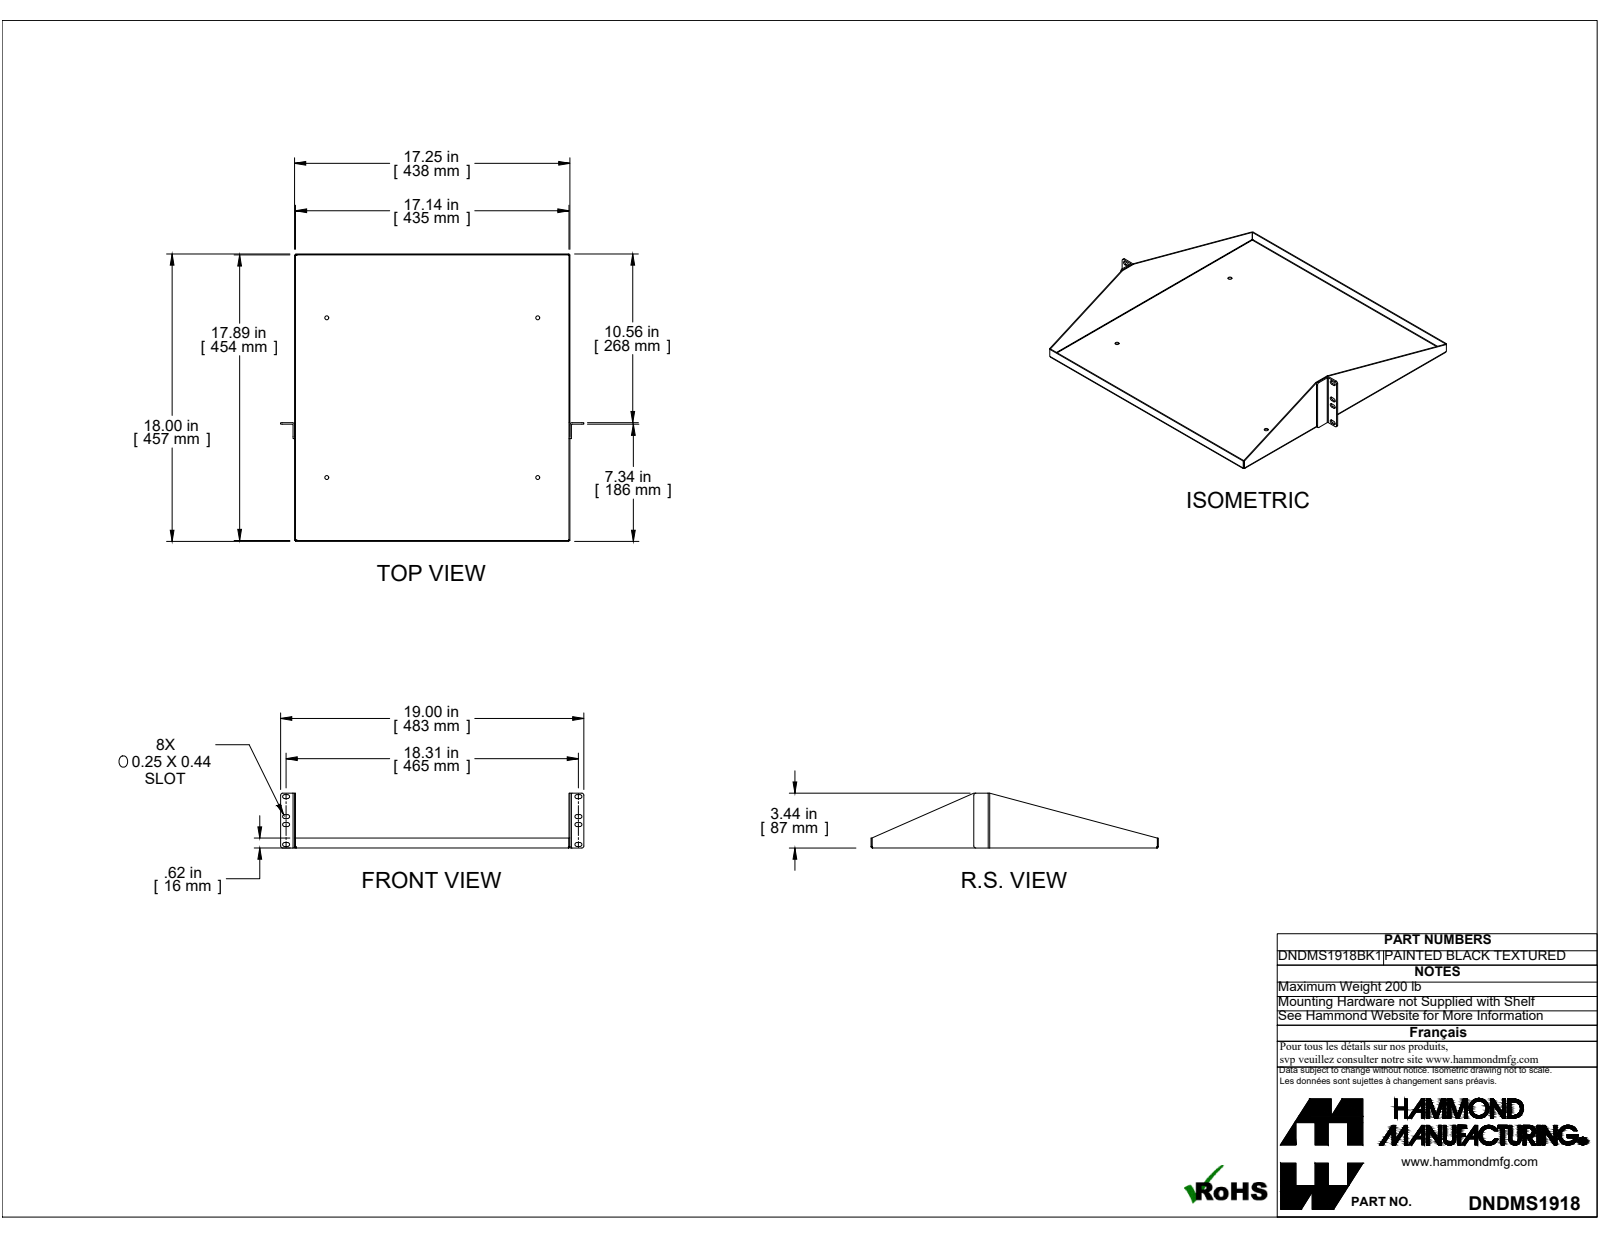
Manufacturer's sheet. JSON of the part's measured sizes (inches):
{"part_name": "DNDMS1918BK1", "step_written_by": "SolidWorks 2019 (CONFIG_CONTROL_DESIGN)", "units": "inches", "bodies": {"solids": 3, "faces": 114, "planar": 58, "cylindrical": 48, "other": 8}, "overall_size": [19, 18, 3.437], "volume_in3": 23.94, "surface_area_in2": 832.5, "round_holes": [[0.25, 4]], "partial_cylinders_radius": [[0.125, 22], [0.029, 4], [0.055, 4], [0.086, 4], [0.048, 2], [0.143, 2]], "face_to_face_distances": [0.057, 0.057, 17.193, 17.25, 17.136, 17.943, 17.886, 18, 0.095, 0.152], "hole_center_spacings": [10, 13.218, 16.575]}
